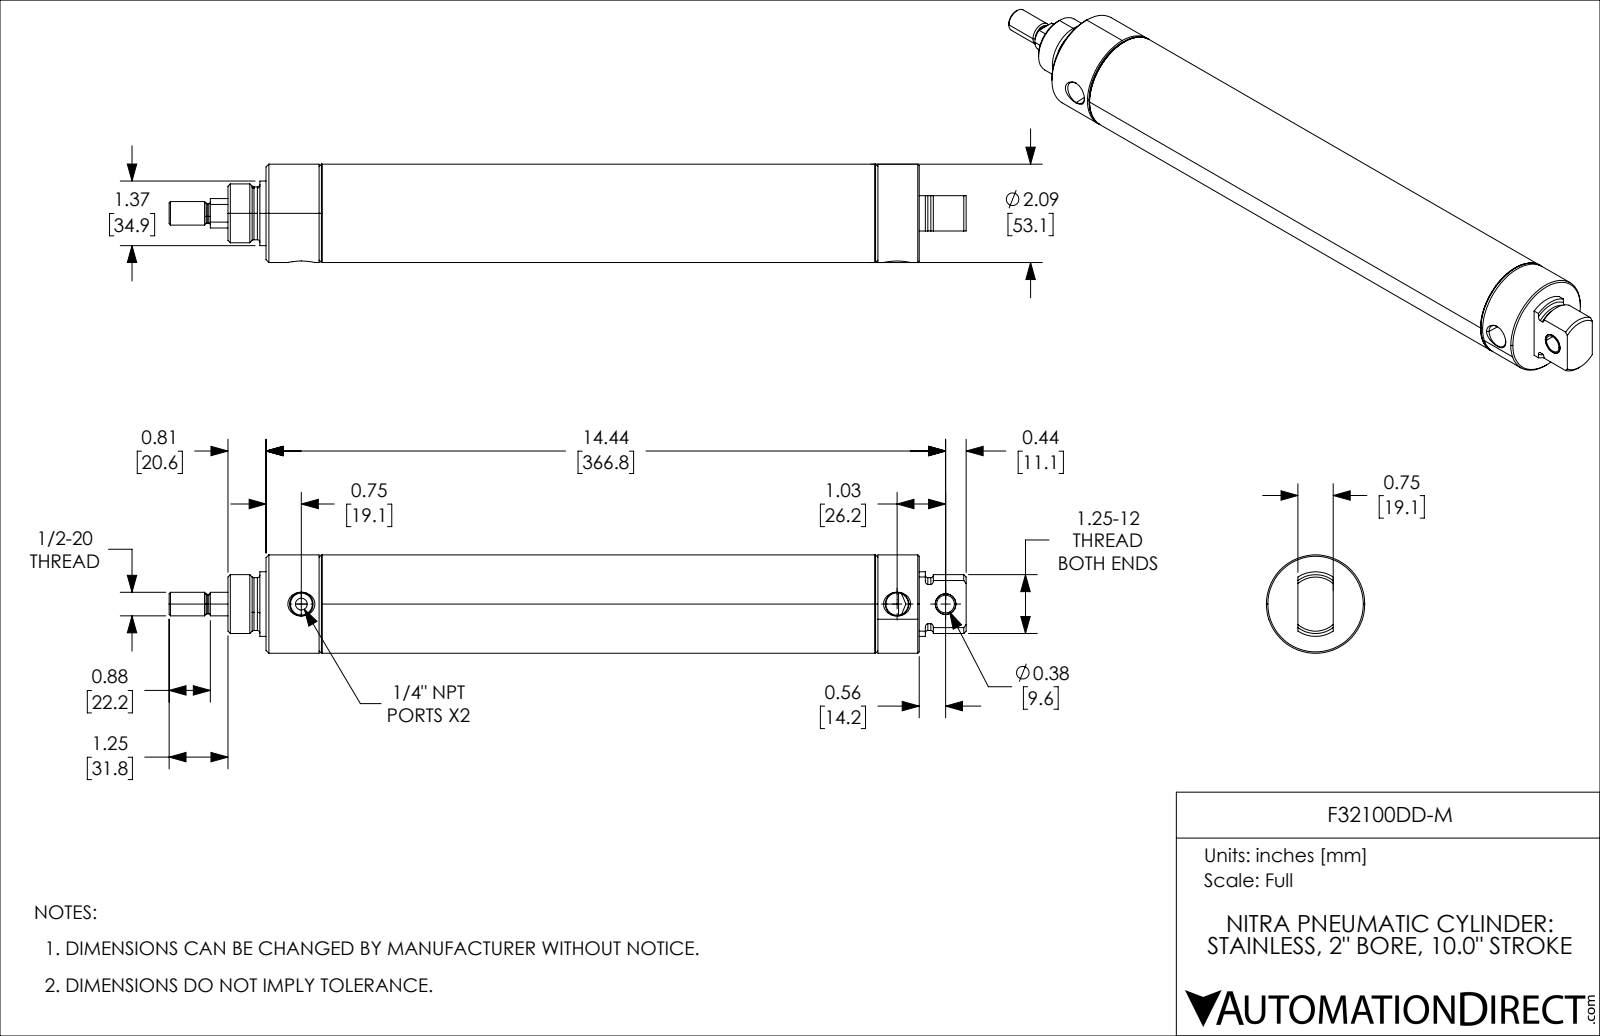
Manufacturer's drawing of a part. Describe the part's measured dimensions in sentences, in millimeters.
The part is named "F32100DD-M_11; F32100DD-M_9; F32100DD-M_5; F32100DD-M_3 (+2 more)". Its 3-D file was written by "SolidWorks 2021 (CONFIG_CONTROL_DESIGN)". It is 5 solids with 160 faces: 31 planar, 60 cylindrical and 69 other. Overall it measures 430.23 by 53.09 by 53.09 millimeters. Its volume is 326 180 cubic millimeters and its surface area 157 901 square millimeters. Round holes: 1 of diameter 6.35, 1 of diameter 9.55, 1 of diameter 11.15, 1 of diameter 12.18, 1 of diameter 16.52, 1 of diameter 19.05, 1 of diameter 49.05. Round bosses or shafts: 1 of diameter 53.09, 1 of diameter 51.16, 1 of diameter 34.87, 1 of diameter 31.75, 1 of diameter 28.51, 1 of diameter 15.88, 1 of diameter 12.7, 1 of diameter 10.46. Partial cylindrical surfaces (rounded edges, fillets, slot ends): 1 of radius 14.25. The main face-to-face distances are 30.17, 254, 284.17, 314.4, 60.4, 30.23, 284.18, 30.18, 30.22, 38.15. The hole center spacings are 26.16, 321.56, 347.72.
